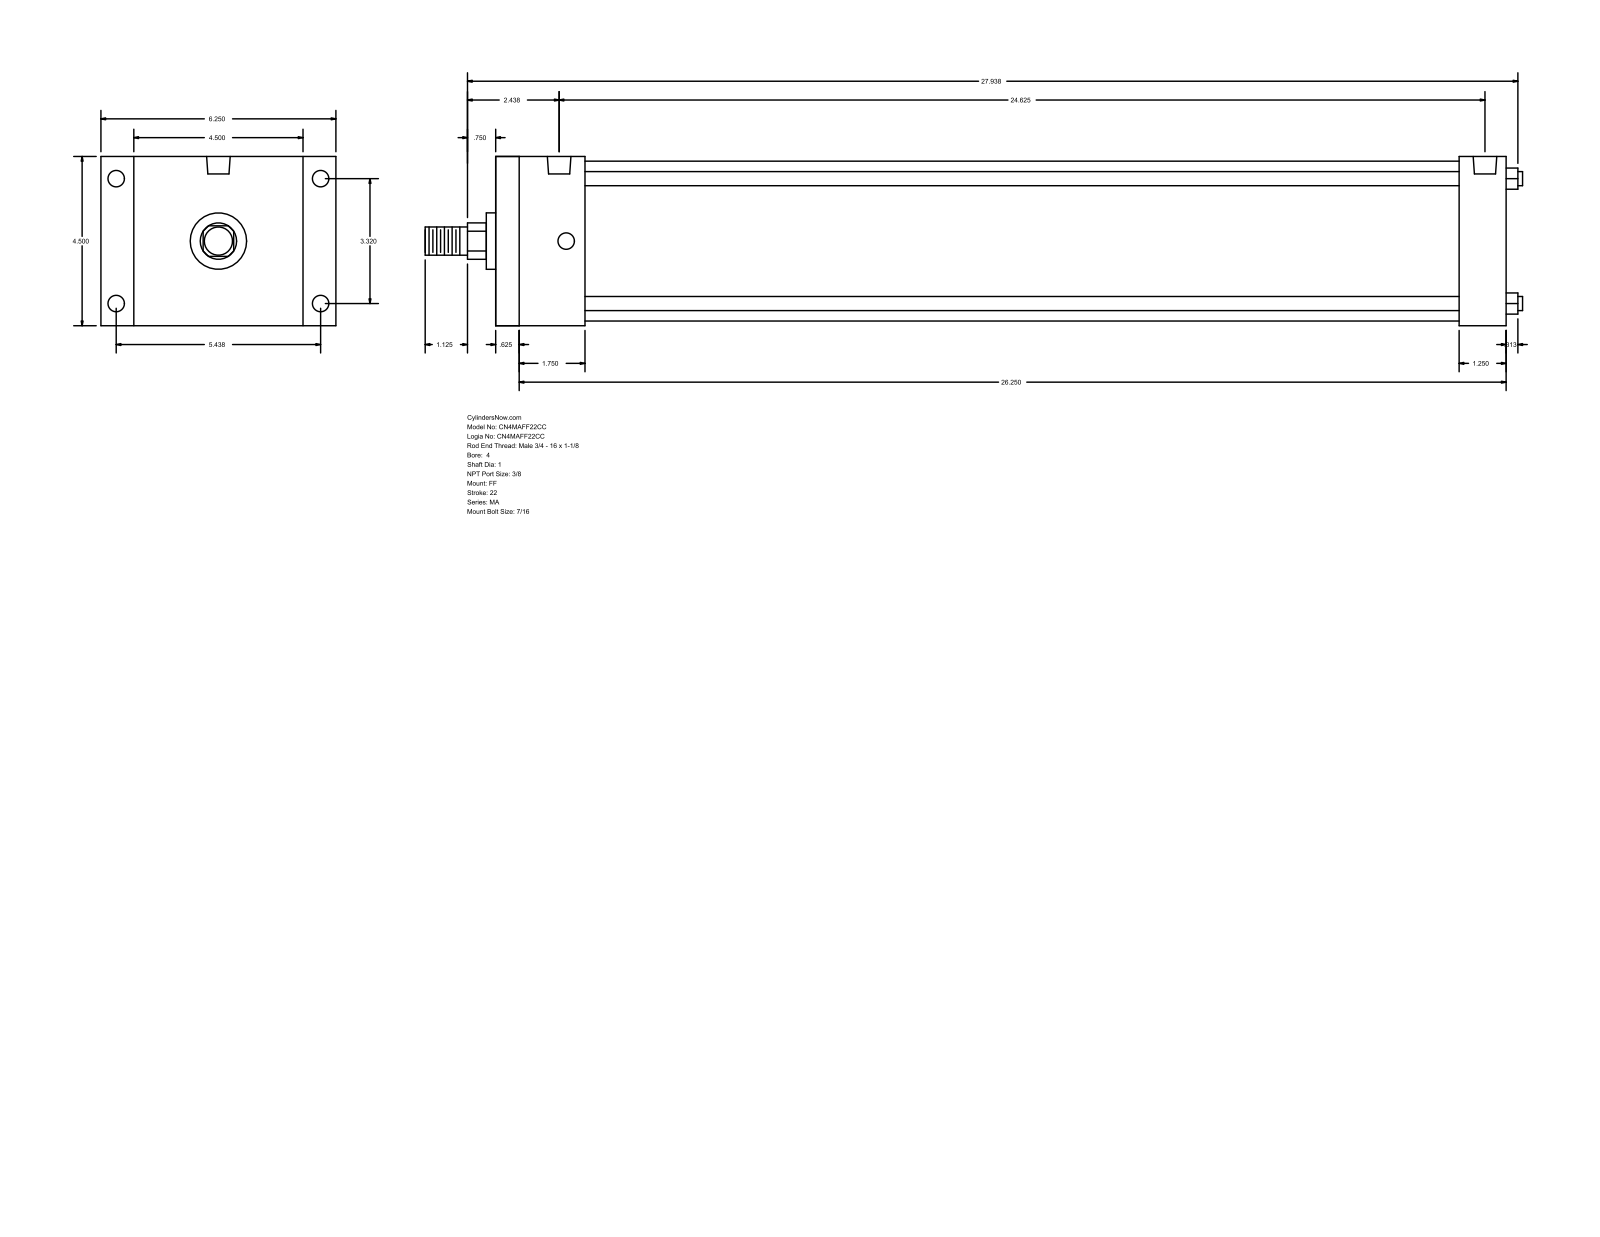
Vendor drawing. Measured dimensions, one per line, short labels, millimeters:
name: MA_FF__0400_1
written by: GSSL Pune (CONFIG_CONTROL_DESIGN)
unit: mm
bodies: 0 solids, 92 faces (64 planar, 28 cylindrical, 0 other)
size: 741.36 × 158.75 × 114.3
holes: 8× ⌀11.11, 2× ⌀15.93
bosses: 4× ⌀9.53, 1× ⌀107.95, 1× ⌀38.1, 1× ⌀25.4, 1× ⌀19.05
rounds: 1× R12.29
face distances: 114.3, 682.62, 15.87, 666.75, 22.23, 136.53, 650.87, 635, 31.75, 60.33
hole spacings: 84.32, 138.12, 161.82, 615.95, 4.76, 4.77, 620.71, 620.72
